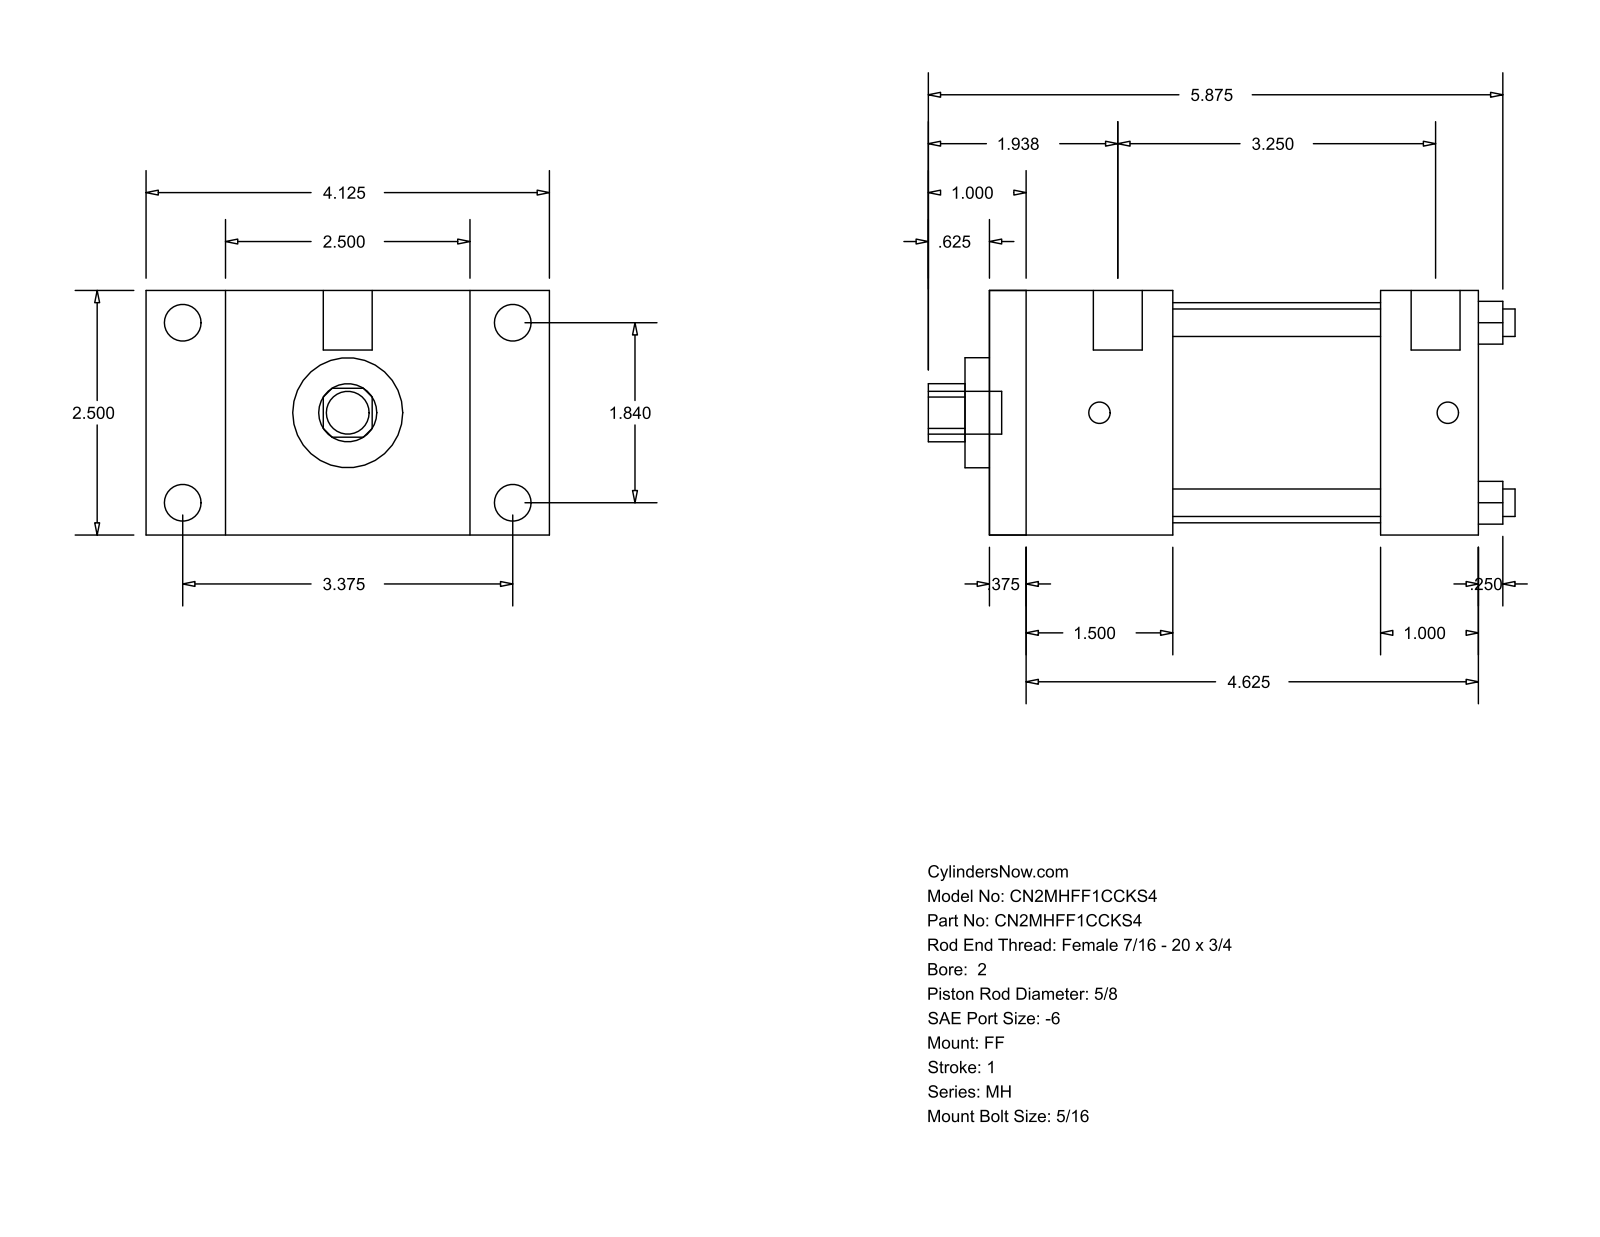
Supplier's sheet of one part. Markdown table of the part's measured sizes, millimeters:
| quantity | value |
| --- | --- |
| part name | MH_FF__0200_0.625 |
| STEP written by | GSSL Pune (CONFIG_CONTROL_DESIGN) |
| units | millimeters |
| bodies | 0 solids, 92 faces (64 planar, 28 cylindrical, 0 other) |
| overall size | 152.4 × 104.78 × 63.5 |
| round holes (diameter × count) | 7.14 × 4, 15.88 × 1, 28.57 × 1, 57.15 × 1 |
| round bosses / shafts (diameter × count) | 9.53 × 4, 5.56 × 4, 12.7 × 2, 11.11 × 1 |
| partial cylindrical surfaces (radius × count) | 7.54 × 1 |
| main face-to-face distances | 63.5, 127, 9.52, 117.48, 53.97, 38.1, 47.62, 101.59, 92.07, 79.38 |
| hole center spacings | 33.05, 46.74, 66.1 |
